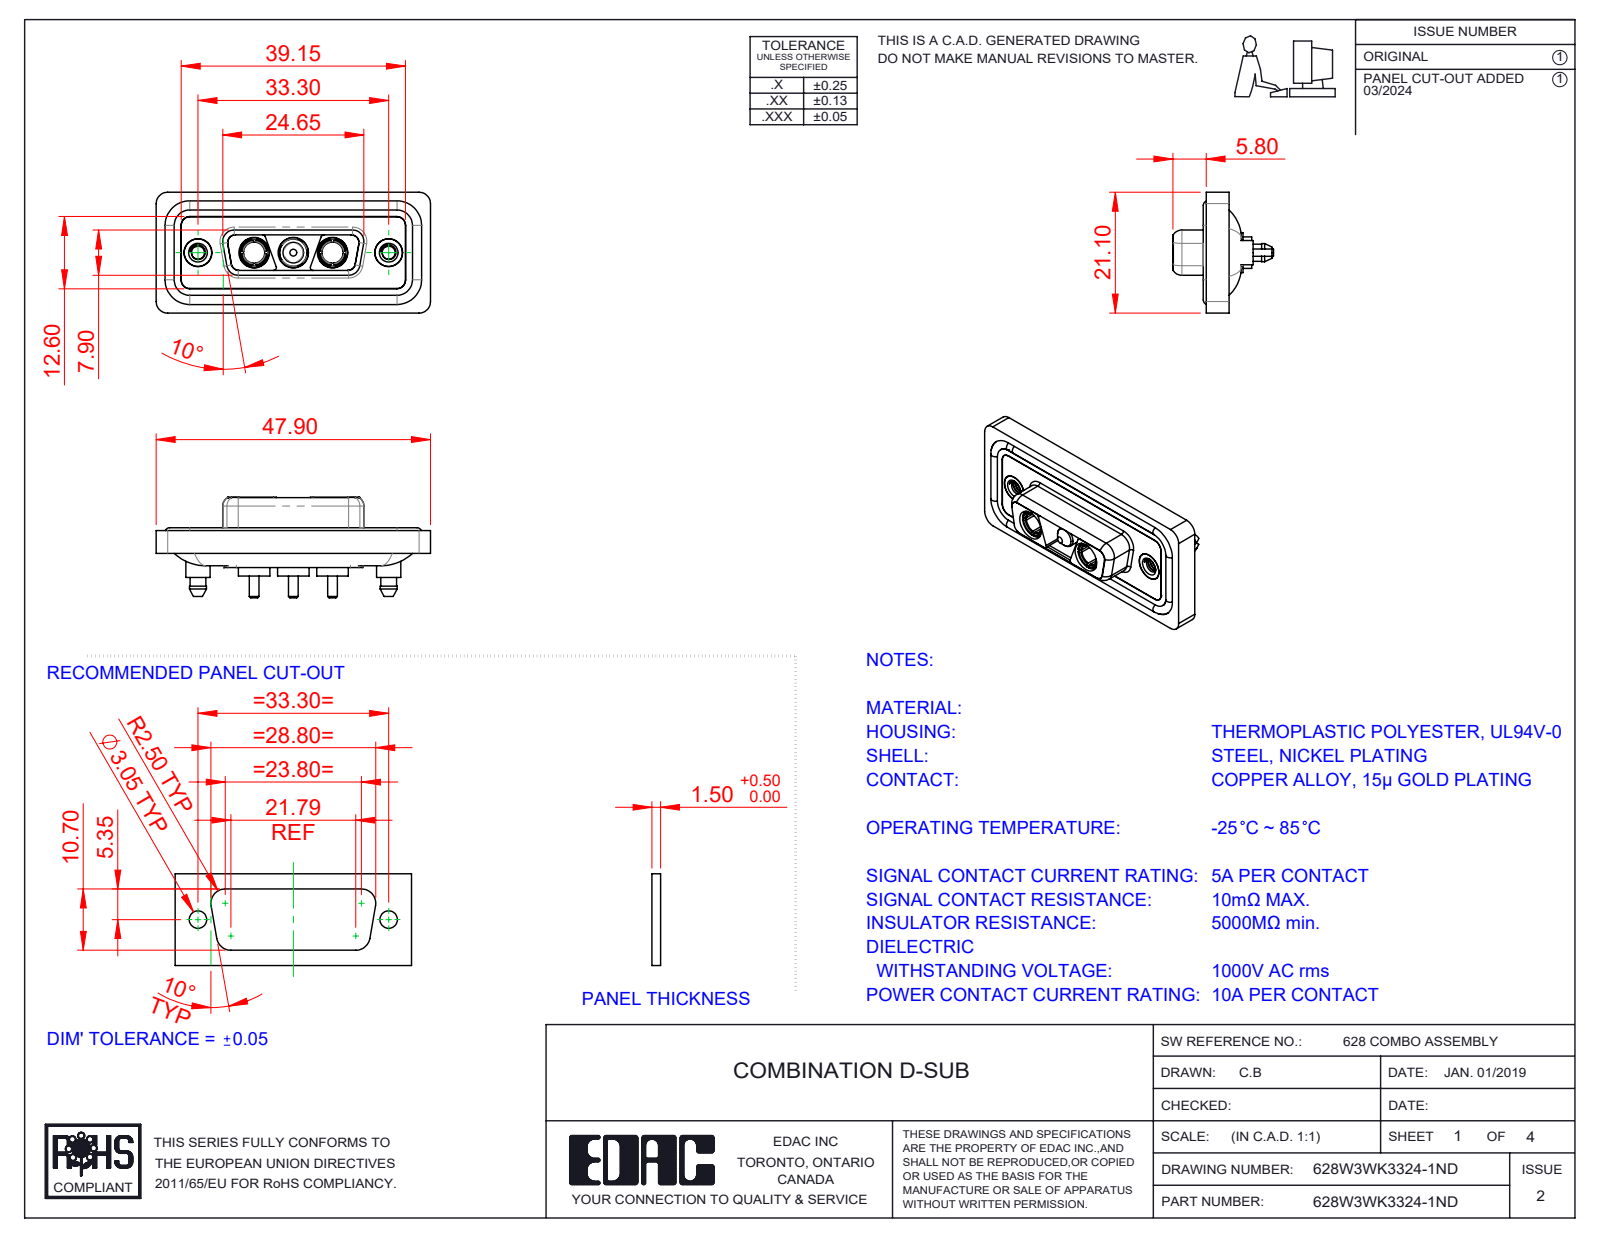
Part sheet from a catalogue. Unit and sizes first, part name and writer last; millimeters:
Units: millimetres
Overall size (bounding box): 47.9 × 21.1 × 17.55
Round holes (diameter × count): ⌀4.85 ×5, ⌀5.3 ×3, ⌀2.26 ×2, ⌀3.7 ×2, ⌀4 ×2, ⌀4.05 ×2, ⌀5 ×2
Round bosses / shafts (diameter × count): ⌀1.6 ×4, ⌀5.5 ×3, ⌀5.2 ×3, ⌀4.75 ×3, ⌀3.75 ×3, ⌀1.7 ×3, ⌀5.4 ×2, ⌀4.96 ×2
Partial cylindrical surfaces — rounded edges, fillets, slot ends (radius × count): R1.5 ×24, R2 ×20, R1.35 ×12, R1.6 ×10, R0.5 ×8, R0.25 ×4, R0.6 ×4, R0.65 ×4
Main face-to-face distances: 0.4, 1.6, 1.8, 0.5, 1.1, 2.9, 5.65, 7.05, 1.5, 5.35
Hole centre spacings: 6.85, 9.8, 16.65, 23.5, 13.7, 33.3
Volume: 5 969 mm³ · Surface area: 9 806 mm²
Bodies: 13 solids, 649 faces (194 planar, 306 cylindrical, 149 other)
Part name (STEP PRODUCT): 628Combo Shell Front_15 Contacts; 628Combo Waterproof Housing_15 Contacts; 628Combo Housing_3WK3; Power Pin_10A S (+4 more)
STEP written by: SolidWorks 2023 (CONFIG_CONTROL_DESIGN)
